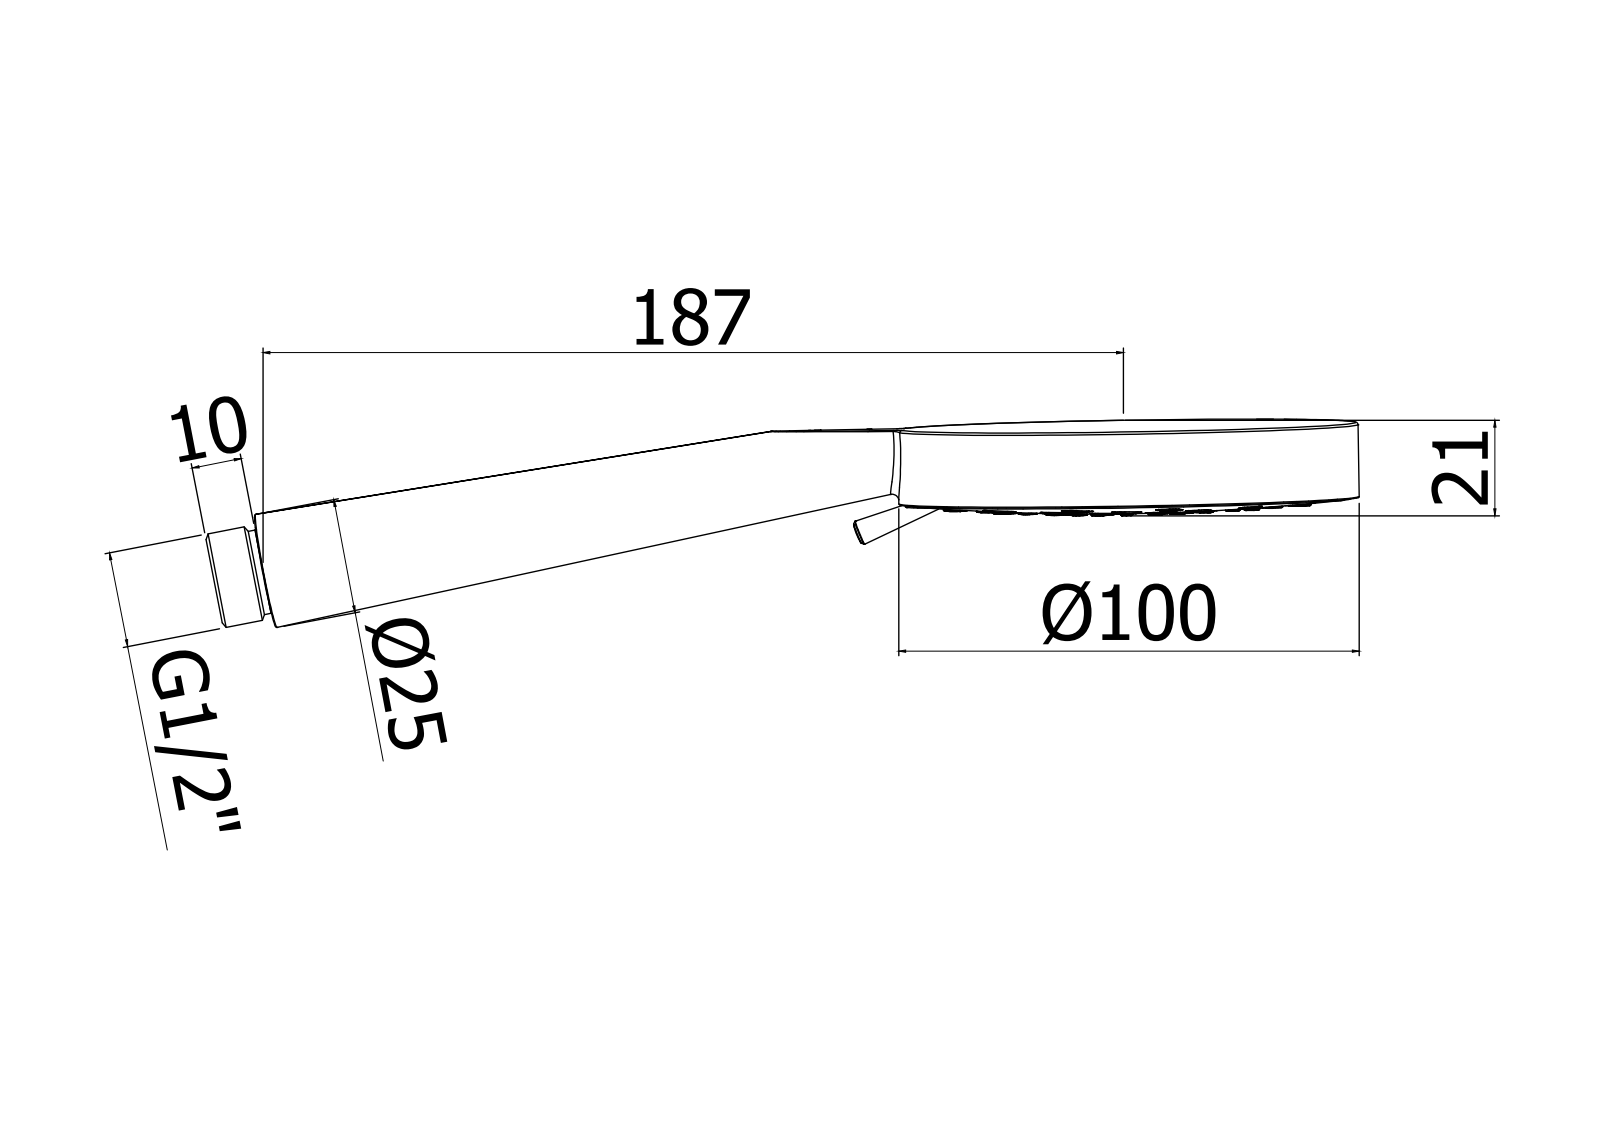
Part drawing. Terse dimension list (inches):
name: 4072038CR_A; 4072038CR_B; 4072038CR_D; 4072038CR_C (+2 more)
written by: CREO PARAMETRIC BY PTC INC, 2020044 (CONFIG_CONTROL_DESIGN)
unit: in
bodies: 1 solid, 4290 faces (415 planar, 1090 cylindrical, 2785 other)
size: 9.817 × 3.937 × 1.613
volume: 1.111 in³; area: 125.5 in²
holes: 48× ⌀0.102, 12× ⌀0.087, 2× ⌀0.126, 1× ⌀0.079, 1× ⌀0.236, 1× ⌀0.472, 1× ⌀1.22, 1× ⌀1.26, 1× ⌀1.496, 1× ⌀3.291, 1× ⌀3.331
bosses: 2× ⌀0.354, 1× ⌀3.937, 1× ⌀3.819, 1× ⌀3.488, 1× ⌀1.457, 1× ⌀1.22, 1× ⌀0.823, 1× ⌀0.724
rounds: 72× R0.02, 48× R0.025, 48× R0.029, 48× R0.031, 48× R0.033, 48× R0.051, 36× R0.043, 36× R0.048
face distances: 0.098, 0.587, 0.488, 0.476, 0.378, 0.111, 0.126, 0.343, 0.224, 0.02
hole spacings: 0.483, 0.483, 0.837, 0.25, 0.683, 0.933, 0.441, 0.734
